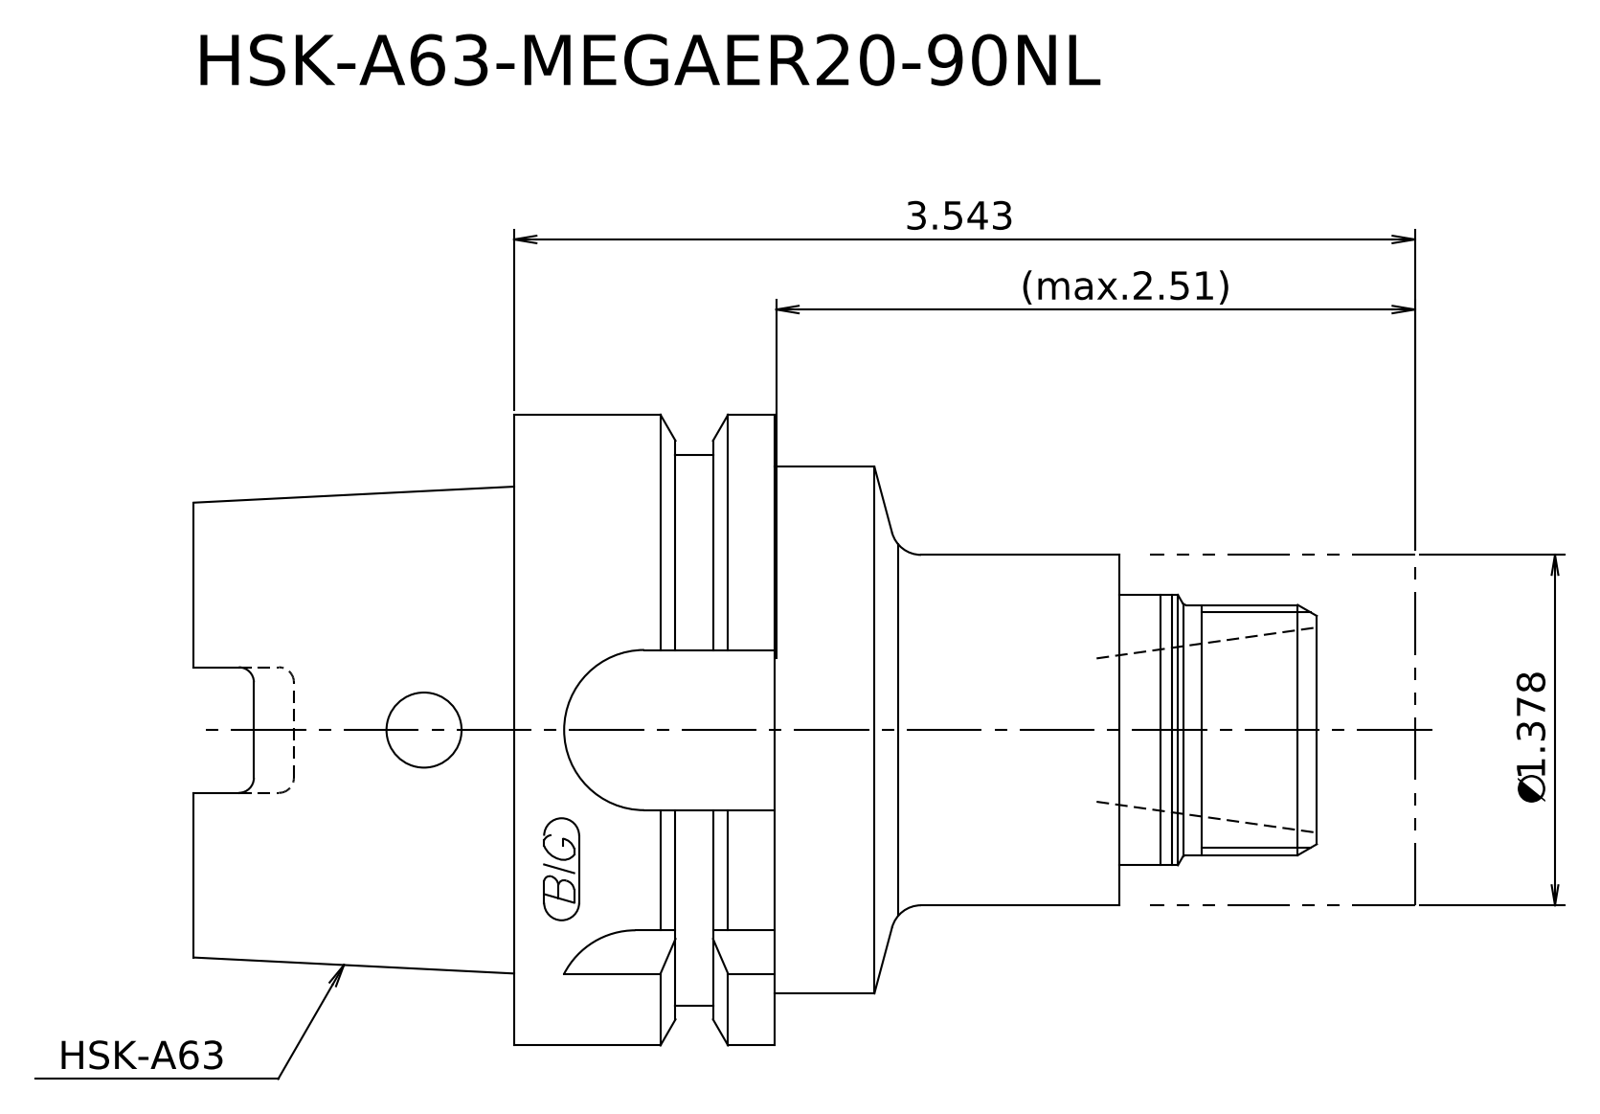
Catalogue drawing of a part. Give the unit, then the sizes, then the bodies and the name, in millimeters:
Units: millimetres
Overall size (bounding box): 122 × 63 × 63
Round bosses / shafts (diameter × count): ⌀63 ×1, ⌀55 ×1, ⌀52.6 ×1, ⌀35 ×1, ⌀27 ×1, ⌀25 ×1
Main face-to-face distances: 32, 63.5, 95.5, 26.5, 90, 122, 64, 37.5, 26, 58
Volume: 216 645 mm³ · Surface area: 27 140 mm²
Bodies: 2 solids, 23 faces (9 planar, 8 cylindrical, 6 other)
STEP written by: Kubotek KeyCreator 2011 V10.0.2 (22737) (automotive_design)
